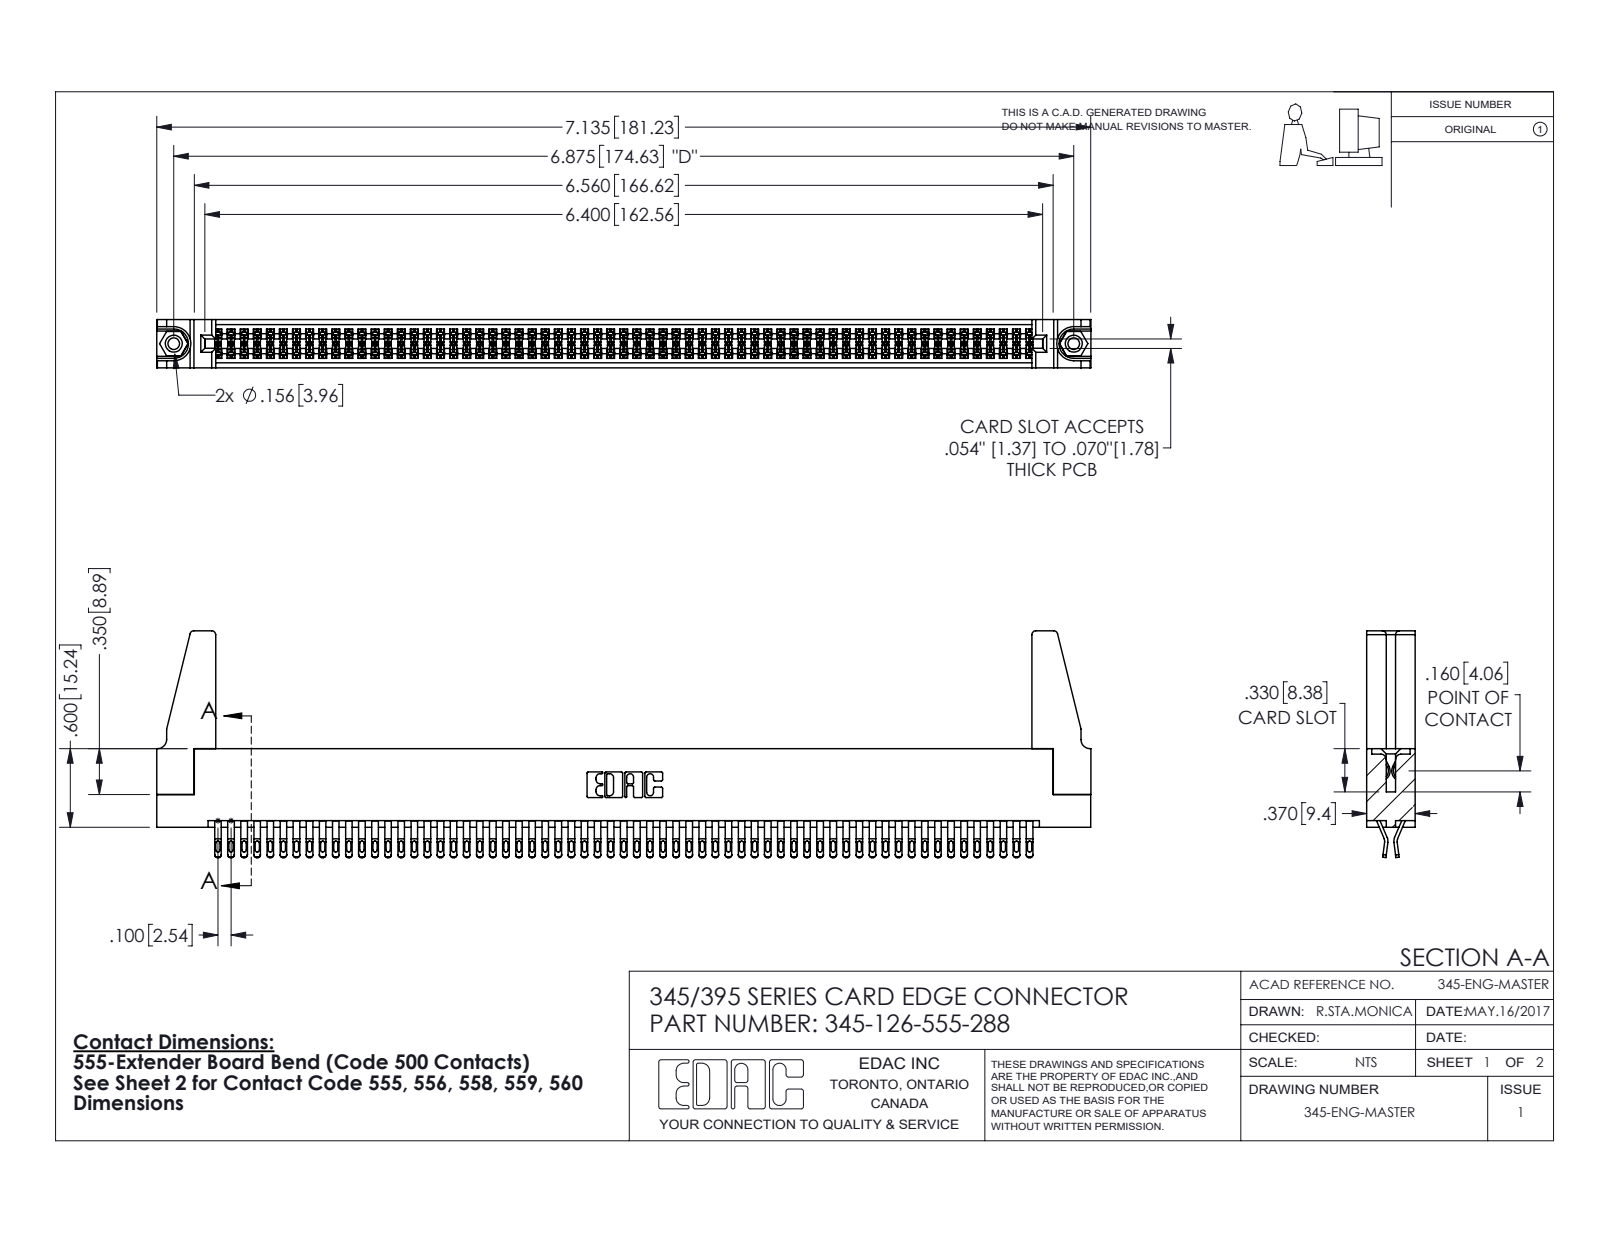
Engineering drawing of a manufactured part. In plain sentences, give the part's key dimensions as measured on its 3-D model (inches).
The part is named "345-250-001_345-250-001-102; 345-292-001_555 Tail; 345 Part_Flush Mounting Lugs - 0.156 Dia-TH; 345-220-078_345-220-088 (+1 more)". Its 3-D file was written by "SolidWorks 2016 (CONFIG_CONTROL_DESIGN)". It is 131 solids with 7306 faces: 4058 planar, 3232 cylindrical and 16 other. Overall it measures 7.136 by 1.732 by 0.37 inches. Its volume is 1.307 cubic inches and its surface area 49.07 square inches. Round holes: 2 of diameter 0.089, 2 of diameter 0.125, 2 of diameter 0.156, 1 of diameter 0.064. Round bosses or shafts: 2 of diameter 0.155. Partial cylindrical surfaces (rounded edges, fillets, slot ends): 315 of radius 0.016, 252 of radius 0.02, 189 of radius 0.006, 22 of radius 0.01, 8 of radius 0.03, 6 of radius 0.007, 6 of radius 0.031, 3 of radius 0.026. The main face-to-face distances are 0.072, 0.298, 0.37, 0.025, 0.2, 0.098, 0.272, 0.225, 0.175, 0.149. The hole center spacings are 0.27, 6.639, 6.875.
